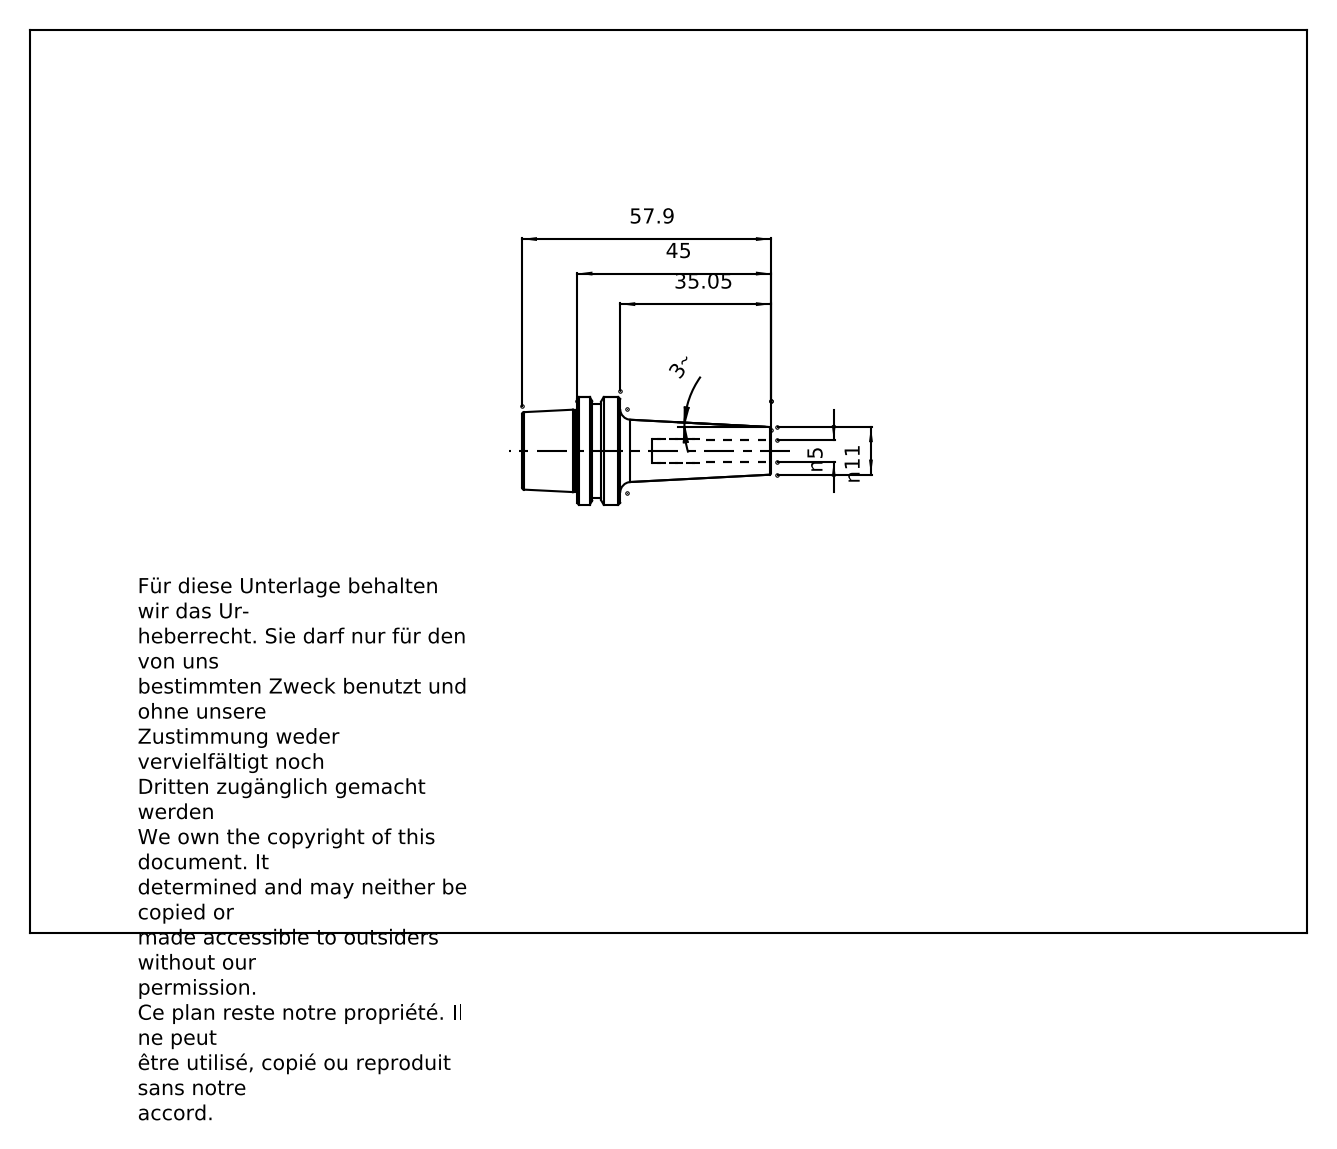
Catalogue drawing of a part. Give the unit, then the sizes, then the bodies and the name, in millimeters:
Units: millimetres
Overall size (bounding box): 57.9 × 25 × 25
Round holes (diameter × count): ⌀5 ×1, ⌀14.04 ×1, ⌀16.45 ×1
Round bosses / shafts (diameter × count): ⌀25 ×1, ⌀21.95 ×1, ⌀18.96 ×1
Main face-to-face distances: 4, 5.95, 9.95, 45, 39.05, 35.05, 12.9, 18.85, 22.85, 57.9
Volume: 8 876 mm³ · Surface area: 5 264 mm²
Bodies: 1 solid, 60 faces (8 planar, 16 cylindrical, 36 other)
Part name (STEP PRODUCT): E25-180-05
STEP written by: PRO/ENGINEER BY PARAMETRIC TECHNOLOGY CORPORATION, 2010430 (CONFIG_CONTROL_DESIGN)
